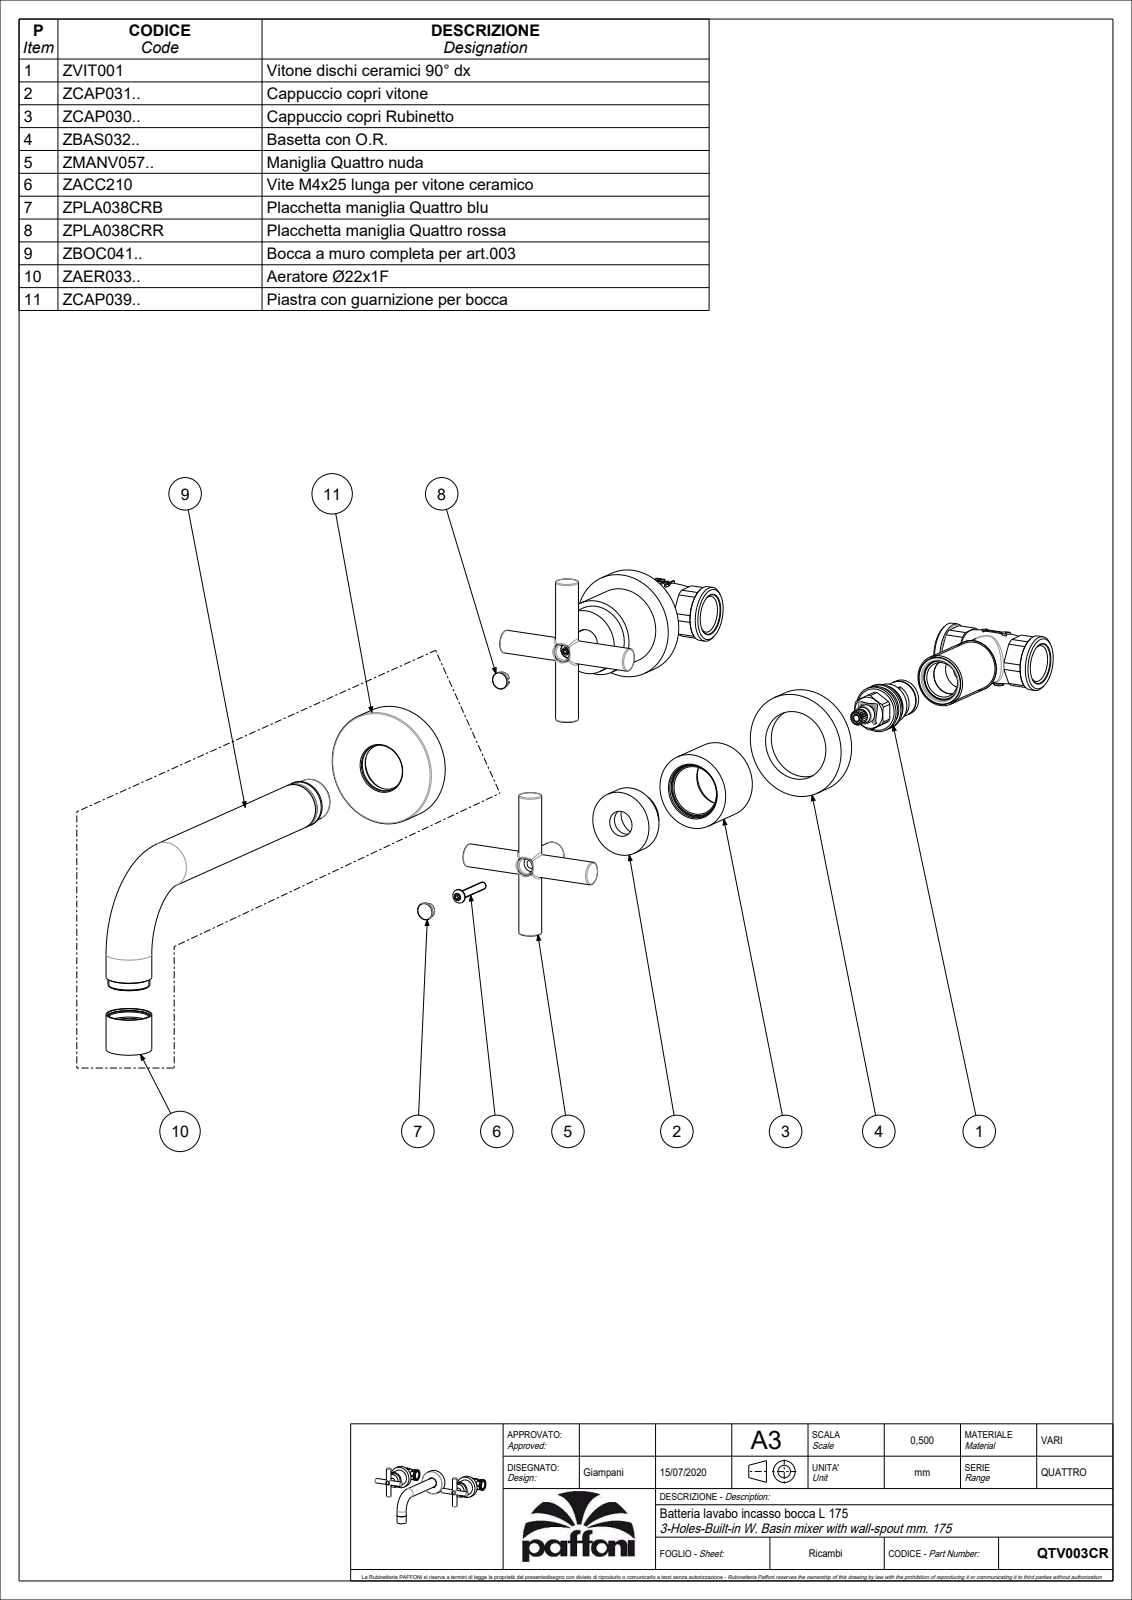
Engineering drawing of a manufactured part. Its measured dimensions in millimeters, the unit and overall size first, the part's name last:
Units: millimetres
Overall size (bounding box): 275 × 183.4 × 108.7
Round holes (diameter × count): ⌀21 ×4, ⌀3.3 ×2, ⌀4.5 ×2, ⌀7 ×2, ⌀8 ×2, ⌀8.5 ×2, ⌀8.8 ×2, ⌀9.5 ×2, ⌀10.3 ×2, ⌀10.5 ×2, ⌀13.5 ×2, ⌀16.3 ×2
Round bosses / shafts (diameter × count): ⌀12 ×3, ⌀55 ×2, ⌀49 ×2, ⌀39.8 ×2, ⌀36 ×2, ⌀34 ×2, ⌀27 ×2, ⌀24 ×2
Partial cylindrical surfaces — rounded edges, fillets, slot ends (radius × count): R0.1 ×34, R0.5 ×4, R1 ×4, R3 ×2, R9.4 ×2
Main face-to-face distances: 4, 11, 15, 1.5, 6, 2.5, 13.5, 5, 44.5, 8.5
Hole centre spacings: 100, 200
Volume: 190 690 mm³ · Surface area: 103 657 mm²
Bodies: 7 solids, 2284 faces (1822 planar, 258 cylindrical, 204 other)
Part name (STEP PRODUCT): QTV003CR
STEP written by: CREO PARAMETRIC BY PTC INC, 2020044 (CONFIG_CONTROL_DESIGN)
